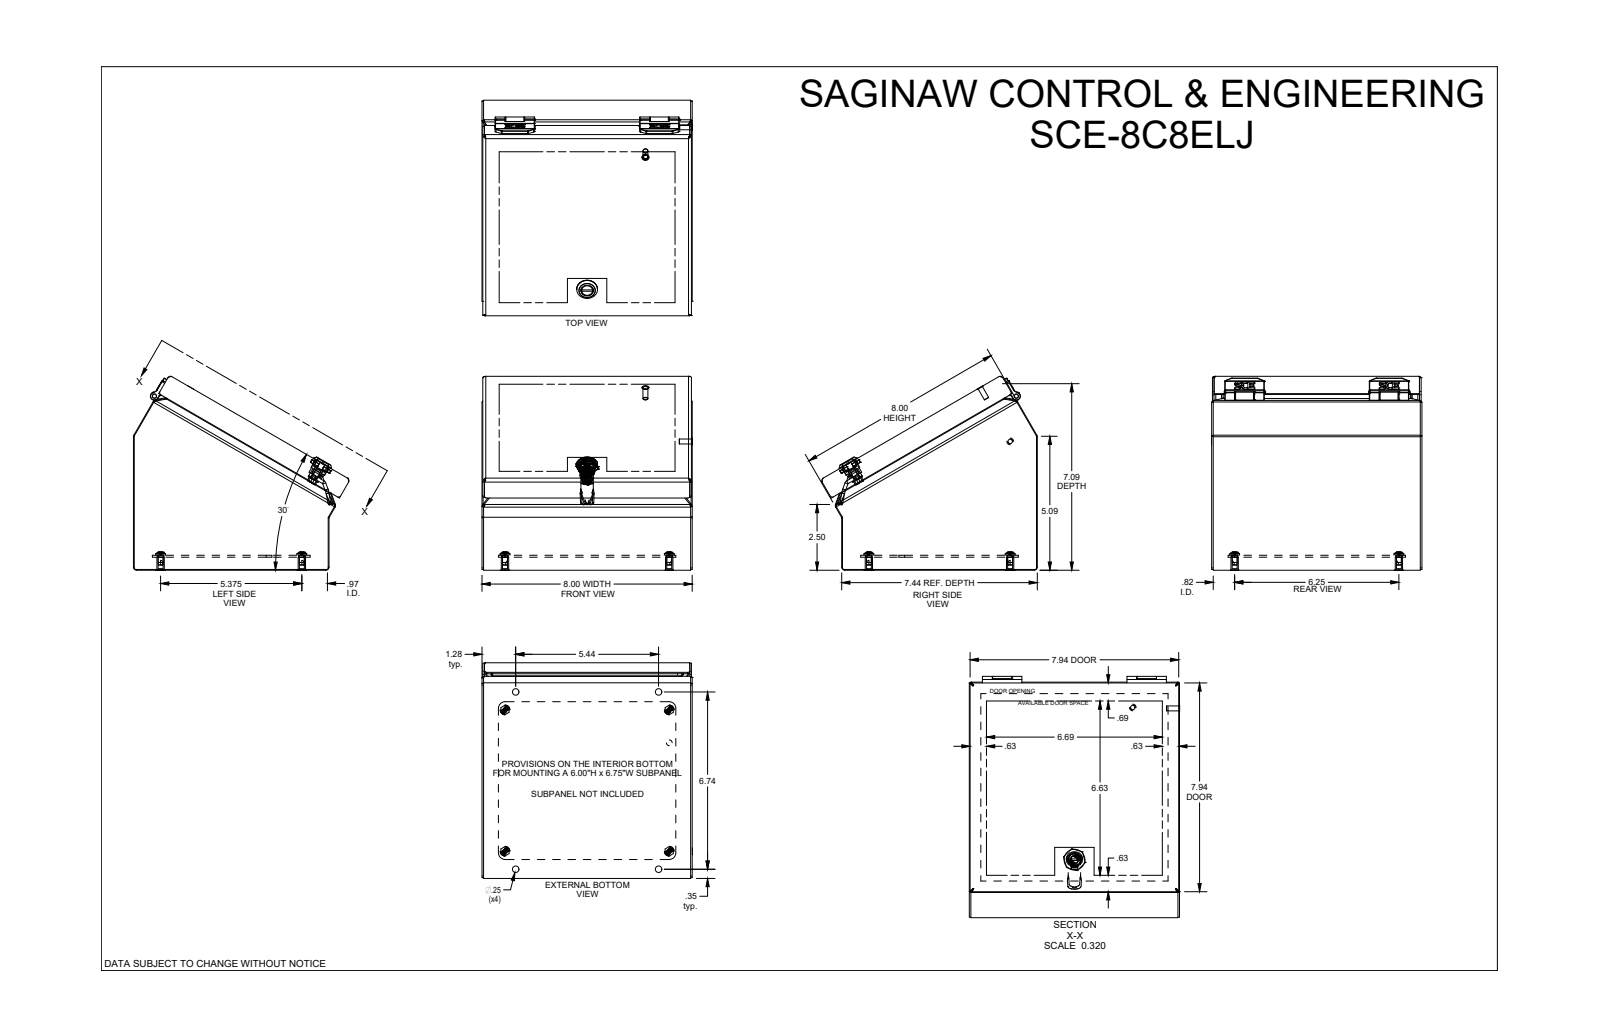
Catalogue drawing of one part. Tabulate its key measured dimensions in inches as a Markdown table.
| quantity | value |
| --- | --- |
| part name | SCE-8C8ELJ |
| STEP written by | SolidWorks 2019 (AUTOMOTIVE_DESIGN) |
| units | inches |
| bodies | 32 solids, 2128 faces (639 planar, 651 cylindrical, 838 other) |
| overall size | 8.201 × 8.004 × 7.38 |
| volume | 24.91 in³ |
| surface area | 781.2 in² |
| round holes (diameter × count) | 0.25 × 8, 0.17 × 4, 0.19 × 4, 0.281 × 4, 0.02 × 2, 0.1 × 2, 0.174 × 2, 0.193 × 2, 0.266 × 2, 0.158 × 1, 0.188 × 1, 0.2 × 1 |
| round bosses / shafts (diameter × count) | 0.188 × 6, 0.479 × 4, 0.373 × 4, 0.28 × 4, 0.26 × 2, 0.256 × 2, 0.18 × 2, 0.788 × 1 |
| partial cylindrical surfaces (radius × count) | 0.106 × 132, 0.005 × 104, 0.008 × 32, 0.025 × 24, 0.03 × 24, 0.06 × 22, 0.013 × 21, 0.015 × 20 |
| main face-to-face distances | 0.06, 0.06, 7.94, 0.511, 0.571, 0.075, 0.436, 0.496, 8, 7.88 |
| hole center spacings | 0.795, 5.884, 6.072, 8.418, 5.375, 5.438, 5.5, 6.198 |
